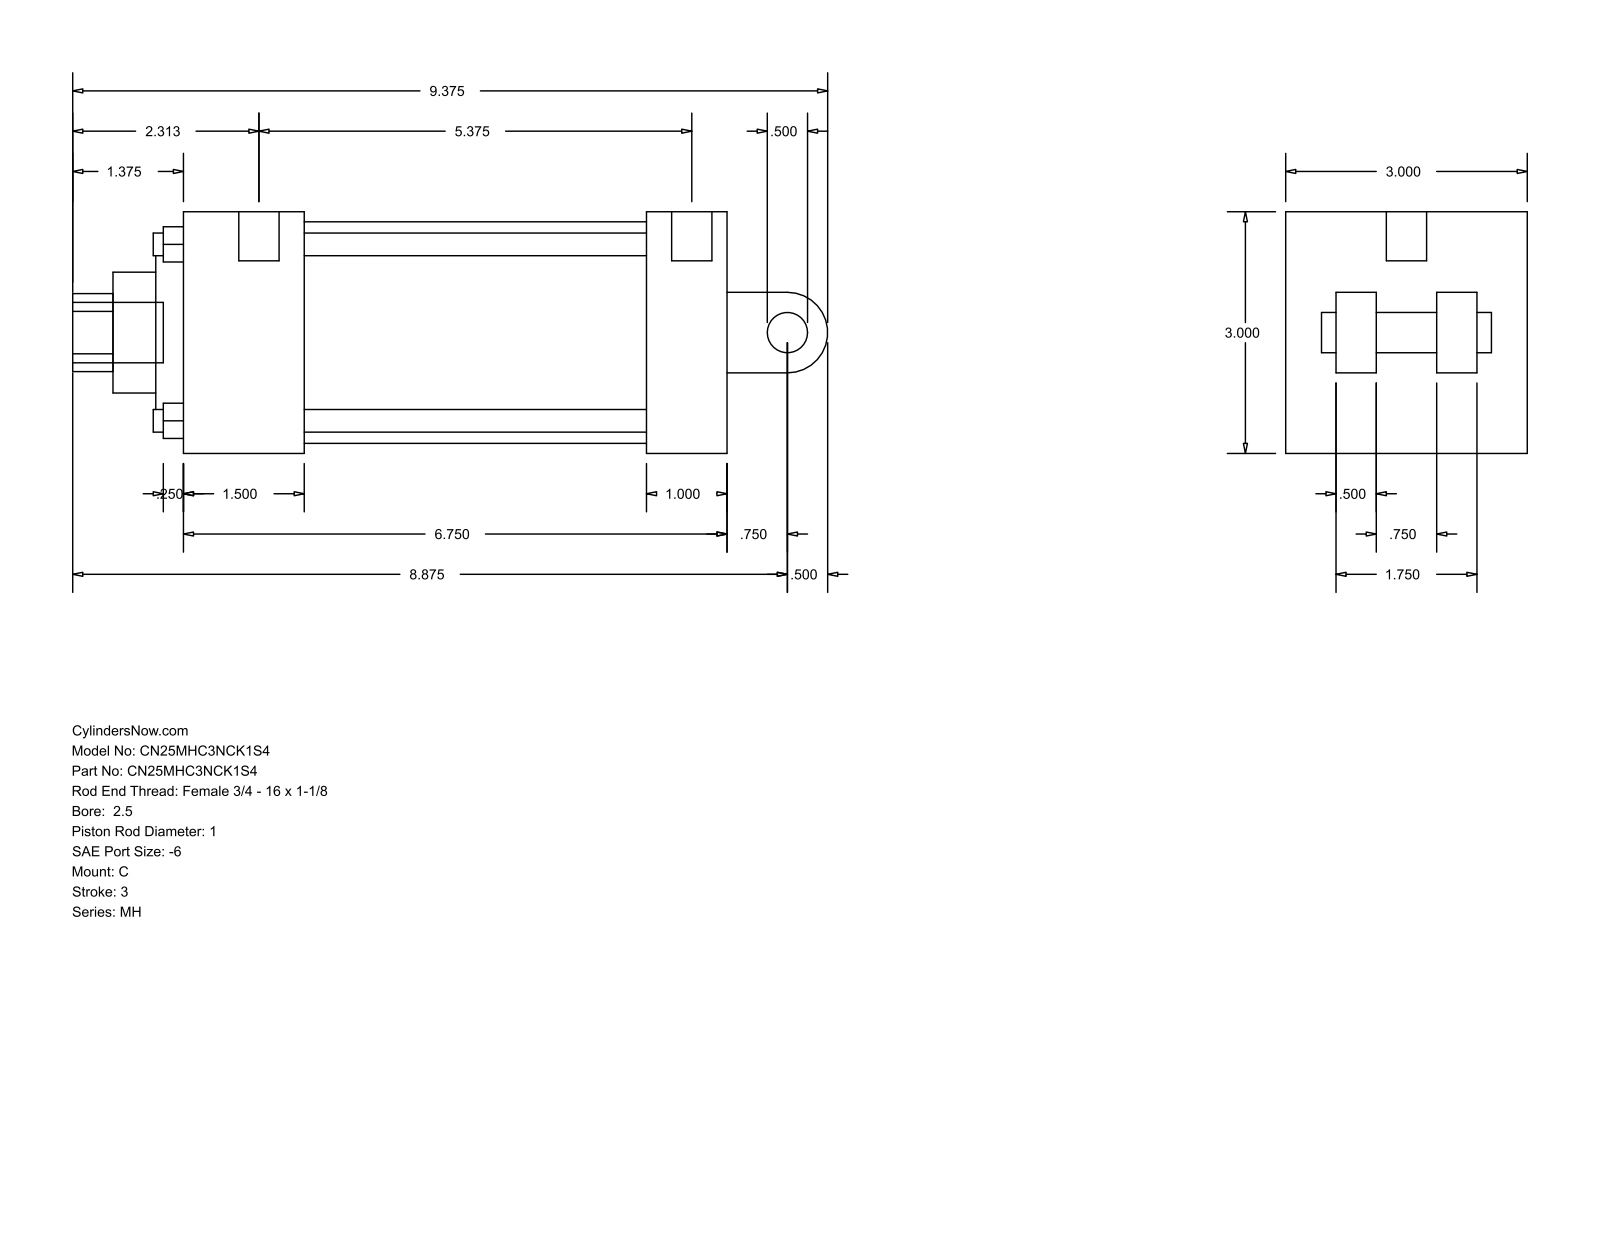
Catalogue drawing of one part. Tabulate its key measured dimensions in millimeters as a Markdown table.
| quantity | value |
| --- | --- |
| part name | MH_C__0250_1 |
| STEP written by | GSSL Pune (CONFIG_CONTROL_DESIGN) |
| units | millimeters |
| bodies | 0 solids, 101 faces (71 planar, 30 cylindrical, 0 other) |
| overall size | 238.12 × 76.2 × 76.2 |
| round holes (diameter × count) | 7.14 × 4, 5.56 × 2, 12.7 × 1, 25.4 × 1, 38.1 × 1, 60.33 × 1, 69.85 × 1 |
| round bosses / shafts (diameter × count) | 12.7 × 2, 5.56 × 2, 19.05 × 1 |
| partial cylindrical surfaces (radius × count) | 12.29 × 1, 12.7 × 1 |
| main face-to-face distances | 76.2, 171.46, 15.87, 60.33, 146.05, 25.41, 38.11, 107.94, 133.35, 12.7 |
| hole center spacings | 39.33, 55.62, 78.66, 3.18 |
